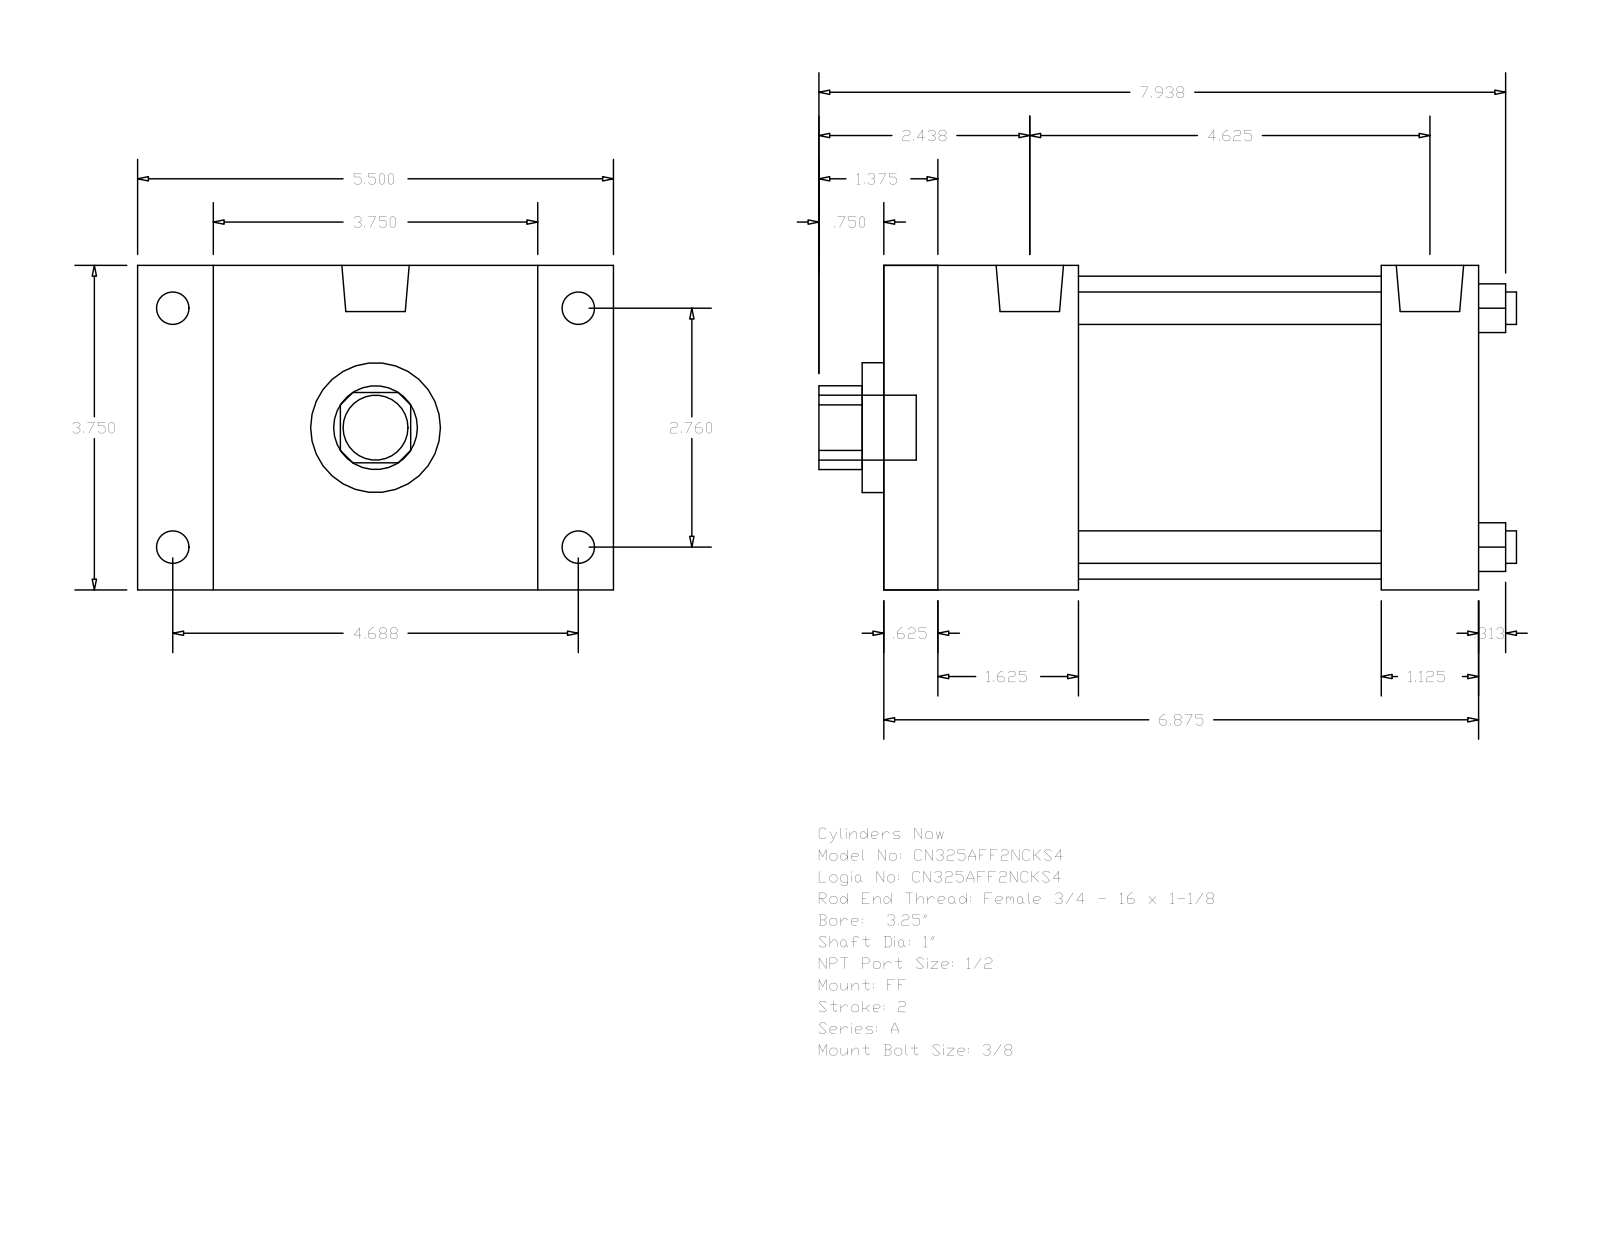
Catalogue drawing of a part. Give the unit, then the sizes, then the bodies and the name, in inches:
Units: inches
Overall size (bounding box): 8.063 × 5.5 × 3.75
Round holes (diameter × count): ⌀0.375 ×4, ⌀1 ×1, ⌀1.5 ×1, ⌀3.5 ×1
Round bosses / shafts (diameter × count): ⌀0.375 ×4, ⌀0.344 ×4, ⌀0.778 ×2, ⌀0.75 ×1
Partial cylindrical surfaces — rounded edges, fillets, slot ends (radius × count): R0.484 ×1
Main face-to-face distances: 3.75, 6.875, 0.625, 6.25, 0.875, 4.625, 2.25, 5.75, 1.625, 5.125
Hole centre spacings: 1.952, 2.76, 3.903
Bodies: 0 solids, 92 faces (64 planar, 28 cylindrical, 0 other)
Part name (STEP PRODUCT): A_FF__0325_1
STEP written by: GSSL Pune (CONFIG_CONTROL_DESIGN)
